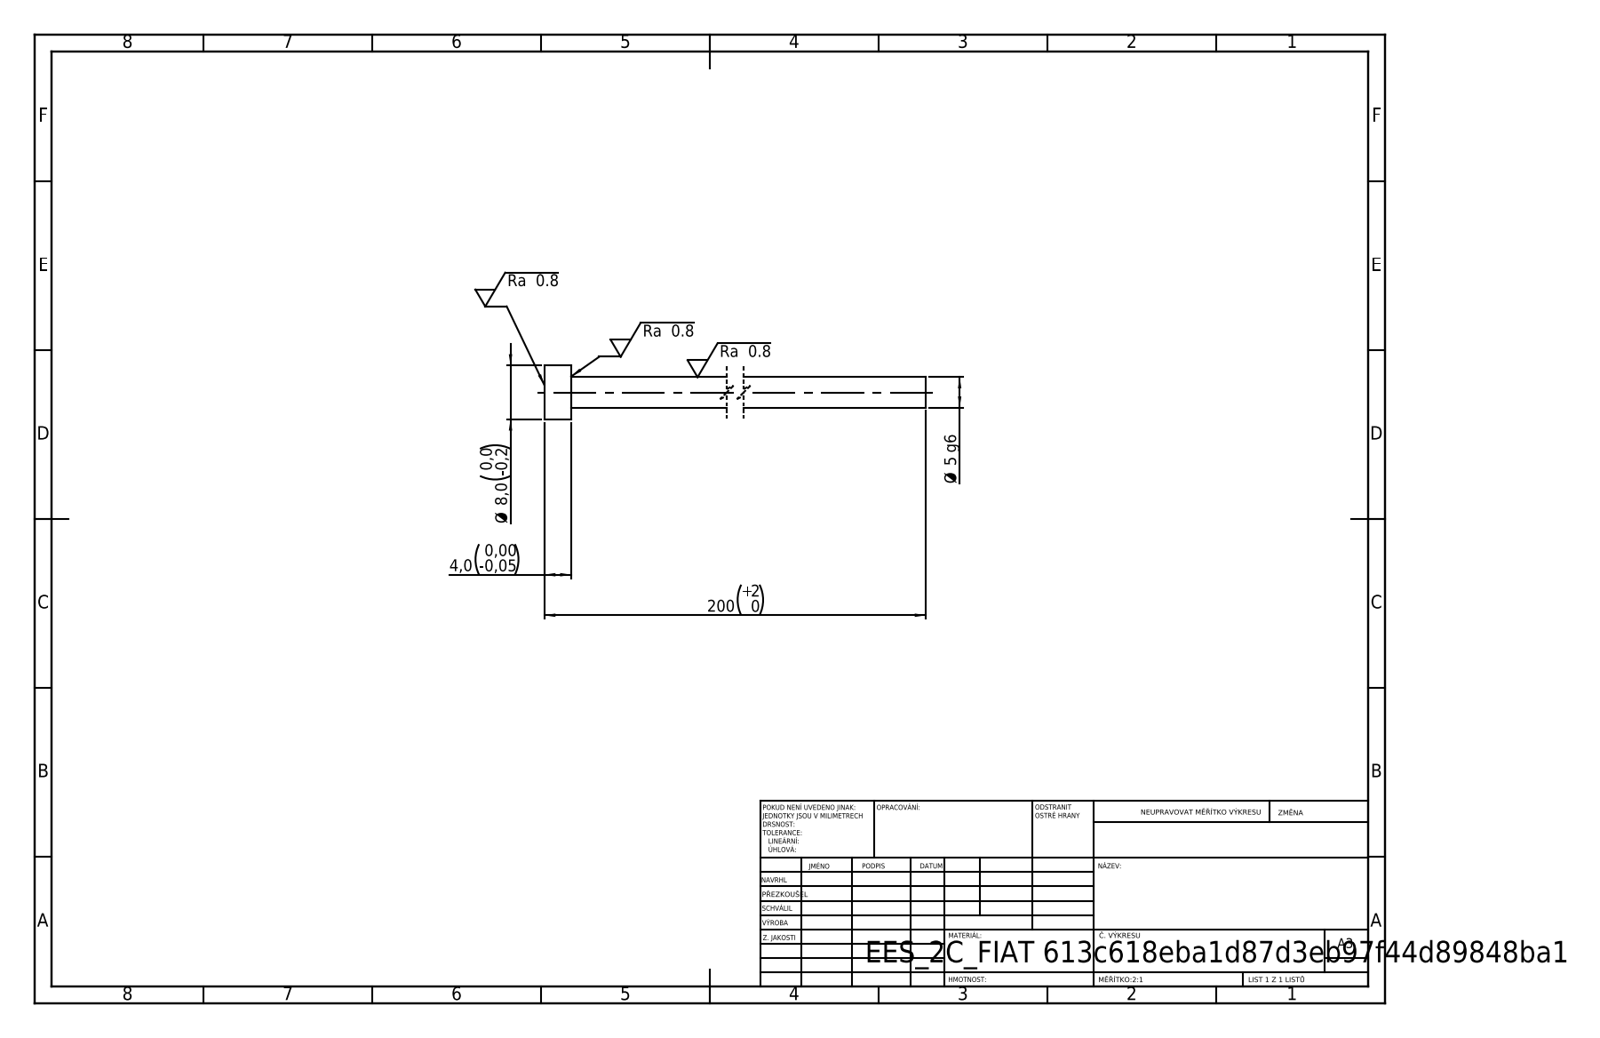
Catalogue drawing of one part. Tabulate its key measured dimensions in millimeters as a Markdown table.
| quantity | value |
| --- | --- |
| STEP written by | SolidWorks 2019 (CONFIG_CONTROL_DESIGN) |
| units | millimeters |
| bodies | 1 solid, 7 faces (3 planar, 4 cylindrical, 0 other) |
| overall size | 200 × 8 × 8 |
| volume | 3 318 mm³ |
| surface area | 2 972 mm² |
| round bosses / shafts (diameter × count) | 8 × 1, 4.5 × 1 |
| main face-to-face distances | 4, 200, 196 |
